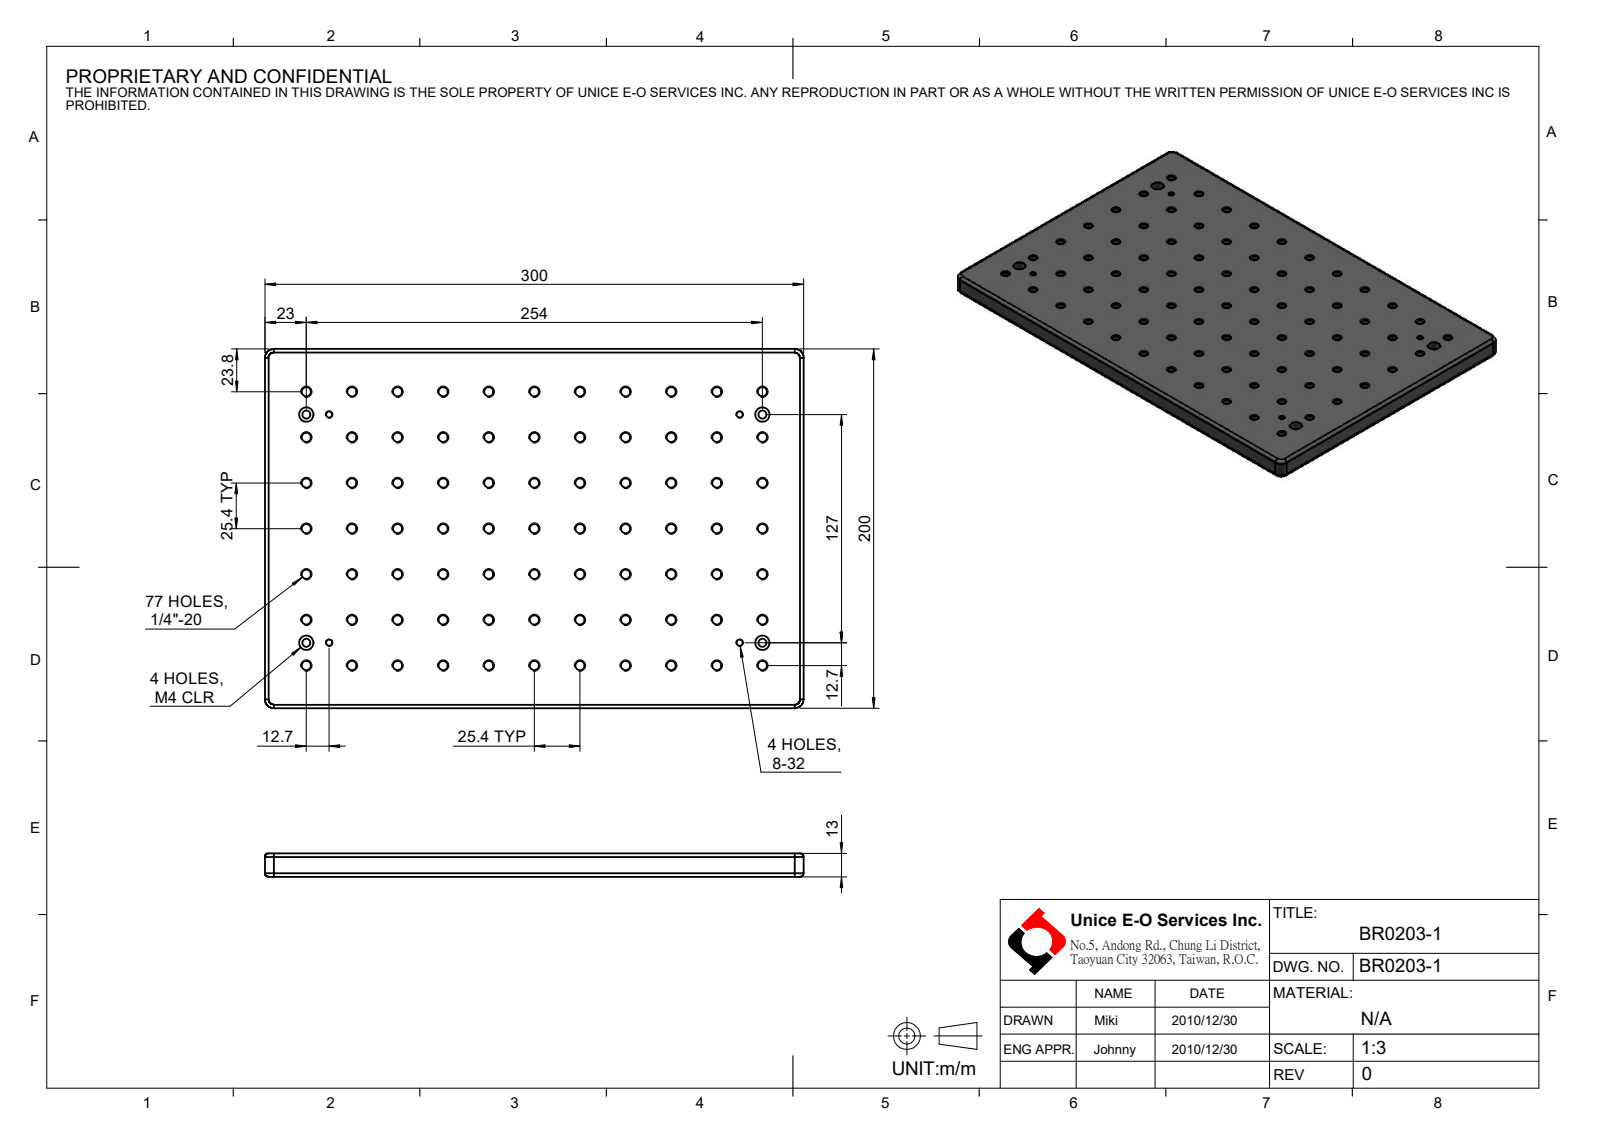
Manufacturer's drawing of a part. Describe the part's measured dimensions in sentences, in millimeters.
The part is named "BR0203-1". Its 3-D file was written by "SolidWorks 2016 (CONFIG_CONTROL_DESIGN)". It is 1 solid with 208 faces: 10 planar, 190 cylindrical and 8 other. Overall it measures 300 by 200 by 13 millimeters. Its volume is 755 393 cubic millimeters and its surface area 145 404 square millimeters. Round holes: 77 of diameter 5.11, 4 of diameter 3.45, 4 of diameter 4.5, 4 of diameter 8. Partial cylindrical surfaces (rounded edges, fillets, slot ends): 8 of radius 2, 4 of radius 5. The main face-to-face distances are 13, 200, 300, 7, 6. The hole center spacings are 25.4, 50.8, 127, 154.5, 76.2, 160.64, 152.4, 170.39.
